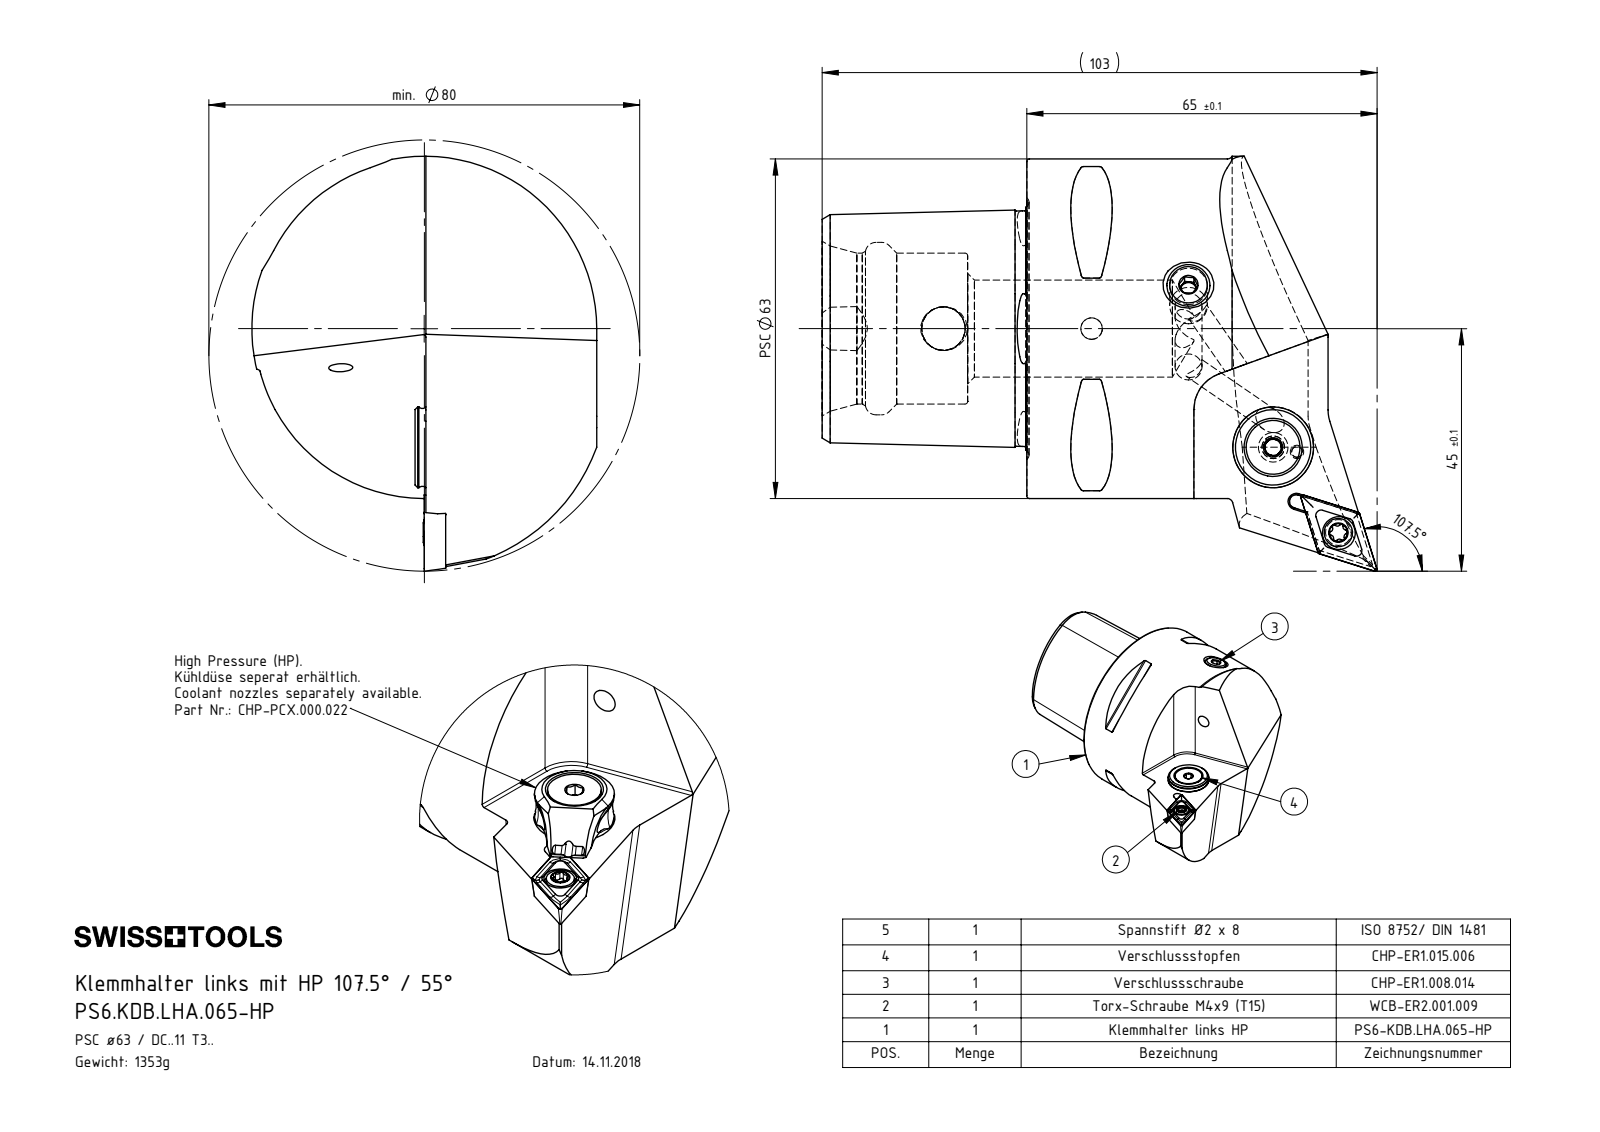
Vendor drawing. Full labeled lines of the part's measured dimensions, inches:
Part name (STEP PRODUCT): CHP-ER1.015.006_A; PS6.KDB.LHA.065-HP; WCB-ER2.001.009_A; DIN 3771 - 13x1 (+6 more)
STEP written by: SolidWorks 2017 (AUTOMOTIVE_DESIGN)
Units: inches
Bodies: 8 solids, 379 faces (91 planar, 100 cylindrical, 188 other)
Overall size (bounding box): 4.056 × 3.031 × 2.52
Volume: 10.49 in³ · Surface area: 48.69 in²
Round holes (diameter × count): ⌀0.165 ×2, ⌀0.197 ×2, ⌀0.047 ×1, ⌀0.079 ×1, ⌀0.098 ×1, ⌀0.118 ×1, ⌀0.13 ×1, ⌀0.157 ×1, ⌀0.173 ×1, ⌀0.205 ×1, ⌀0.24 ×1, ⌀0.276 ×1
Round bosses / shafts (diameter × count): ⌀2.48 ×1, ⌀0.591 ×1, ⌀0.528 ×1, ⌀0.394 ×1, ⌀0.315 ×1, ⌀0.217 ×1, ⌀0.207 ×1, ⌀0.197 ×1
Partial cylindrical surfaces — rounded edges, fillets, slot ends (radius × count): R0.02 ×10, R0.013 ×6, R0.023 ×6, R0.276 ×2, R0.049 ×1, R0.236 ×1, R1.26 ×1, R1.378 ×1
Main face-to-face distances: 1.496, 2.717, 1.22, 1.248, 0.98, 1.071, 0.177, 1.063, 0.433, 1.654
Hole centre spacings: 0.177, 0.662, 0.667, 0.784, 0.789, 1.083, 1.585, 1.751
